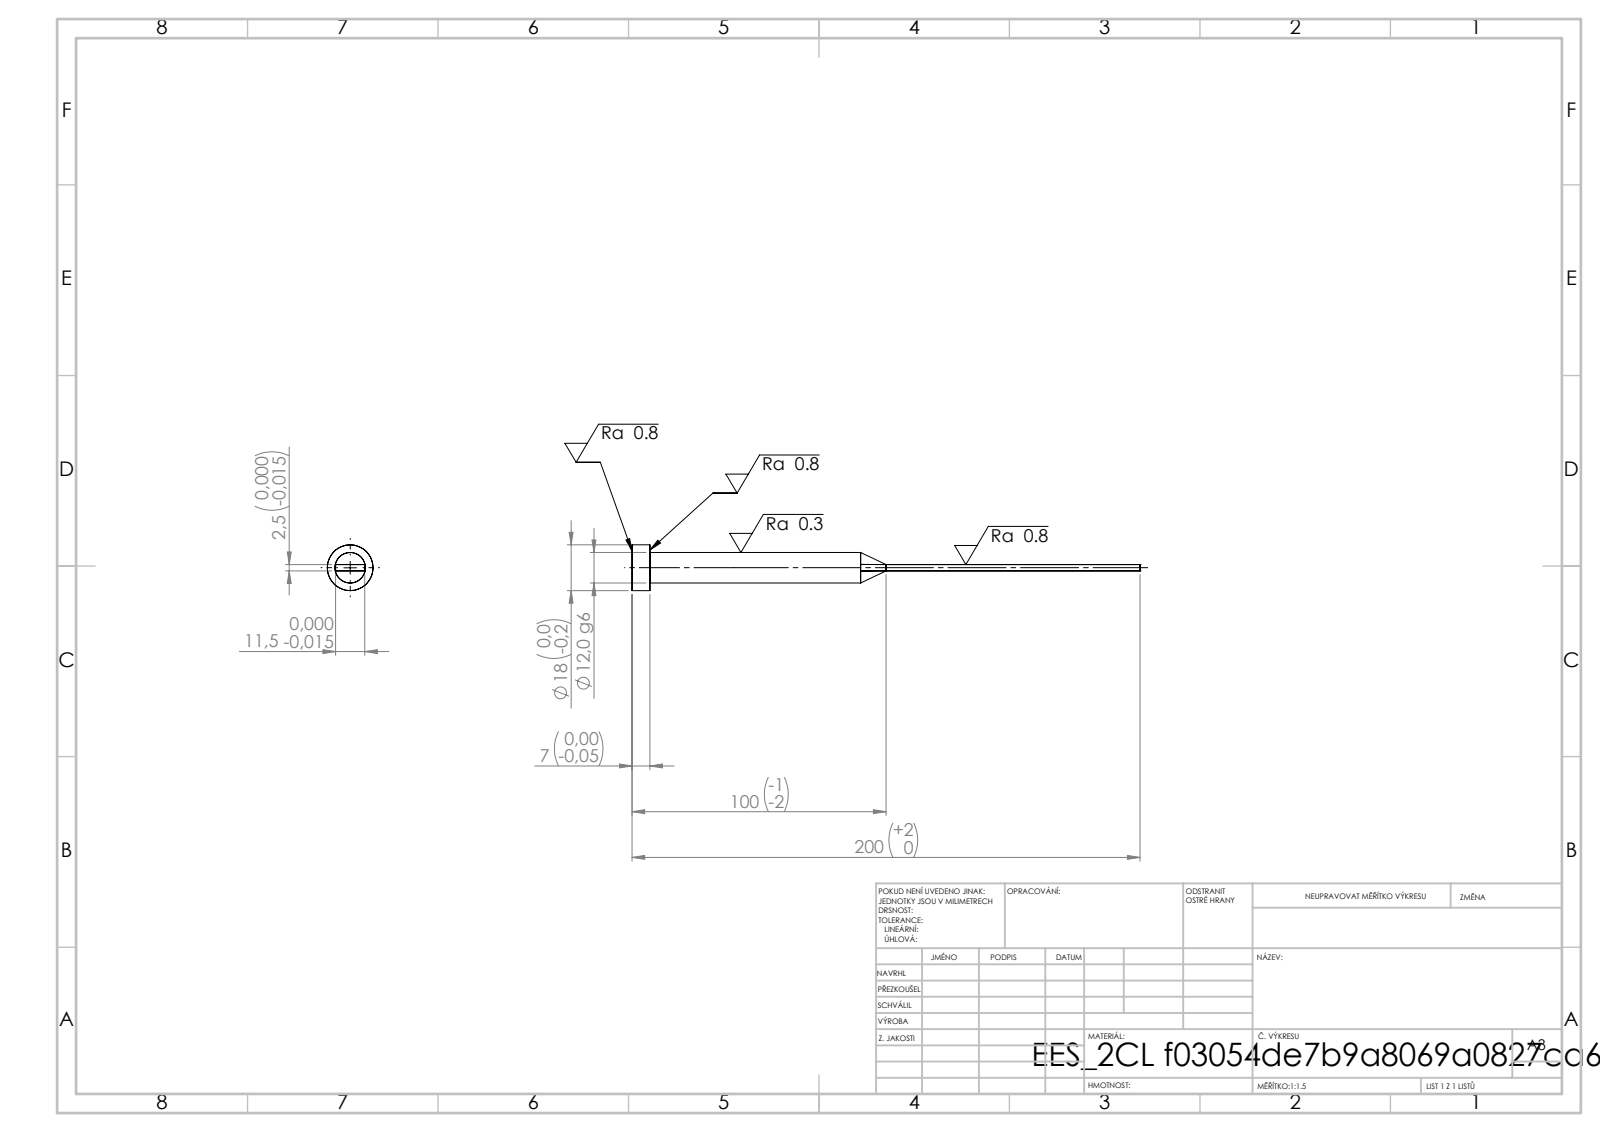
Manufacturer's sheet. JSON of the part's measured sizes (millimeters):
{"step_written_by": "SolidWorks 2019 (CONFIG_CONTROL_DESIGN)", "units": "millimeters", "bodies": {"solids": 1, "faces": 15, "planar": 7, "cylindrical": 4, "other": 4}, "overall_size": [200, 18, 18], "volume_mm3": 14723, "surface_area_mm2": 7079, "round_bosses_or_shafts": [[18, 1], [12, 1]], "face_to_face_distances": [2.5, 11.5, 7, 200, 193]}
